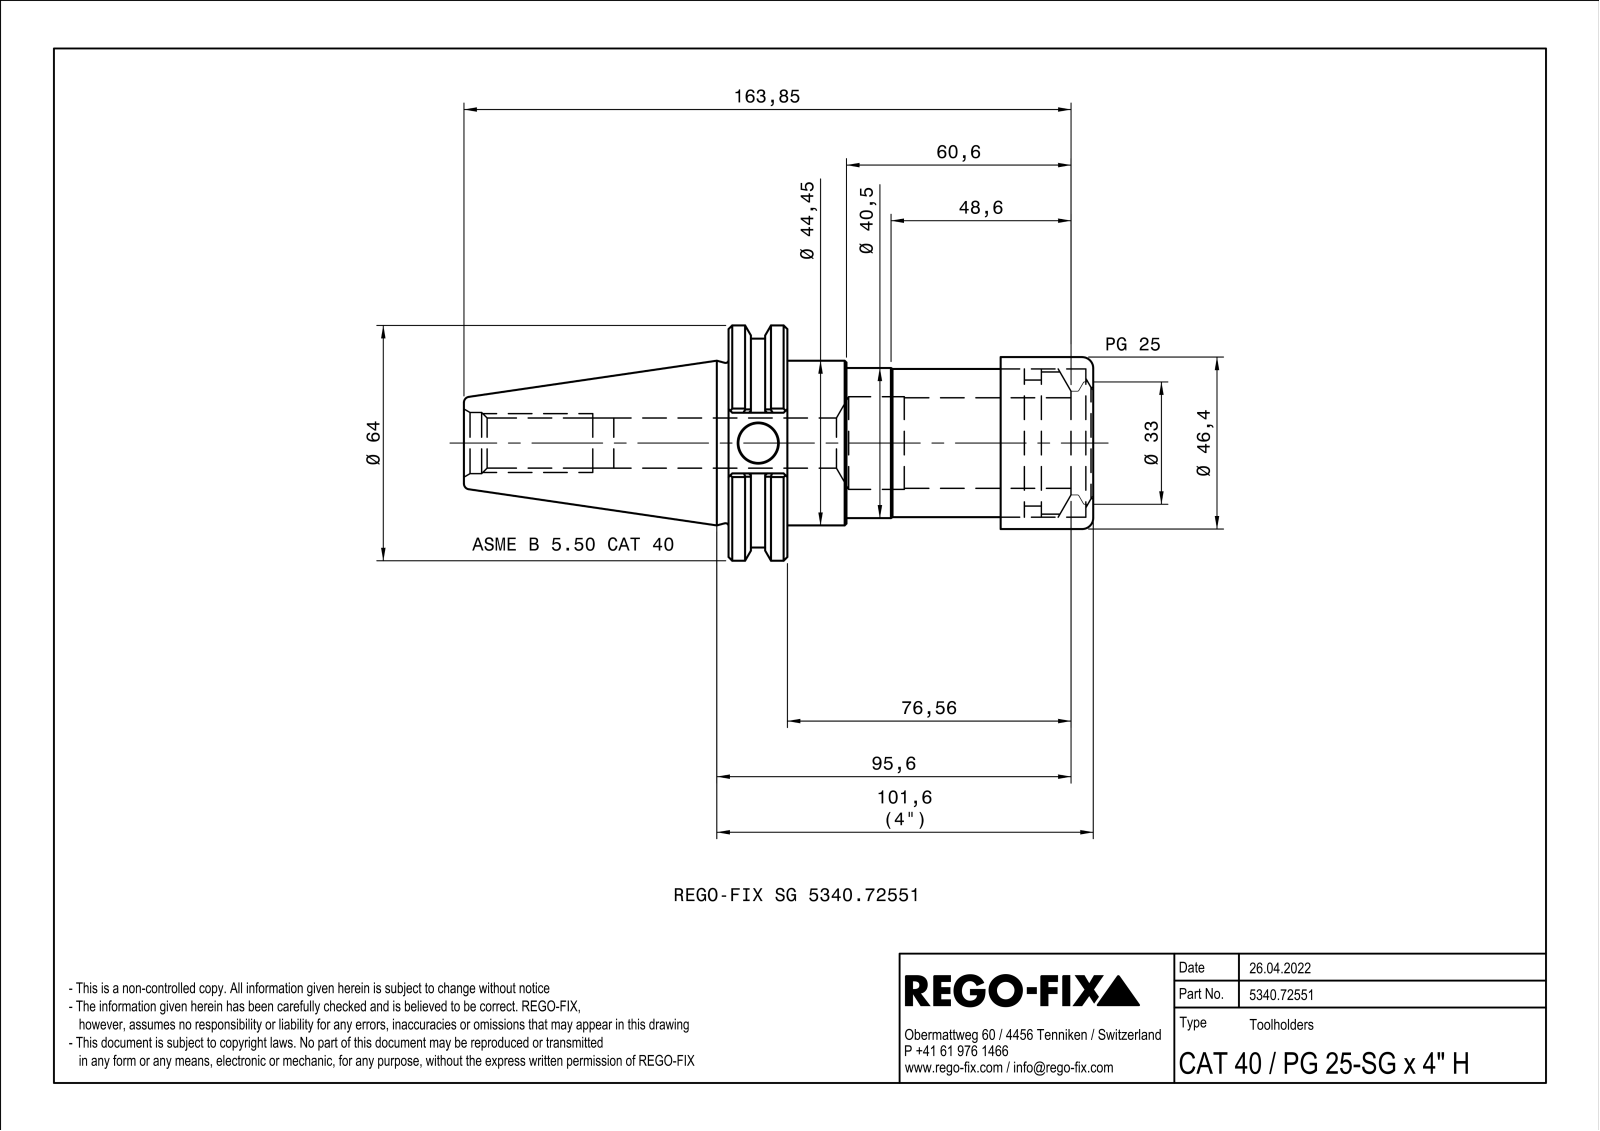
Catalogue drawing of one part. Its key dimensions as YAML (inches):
part_name: "NOCUT"
step_written_by: "SIEMENS PLM Software Solid Edge ST10 (AUTOMOTIVE_DESIGN)"
units: inches
bodies: {solids: 1, faces: 110, planar: 37, cylindrical: 23, other: 50}
overall_size: [6.687, 2.5, 2.393]
volume: 10.79
surface_area: 65.96
round_holes:
  - {diameter: 0.421, count: 1}
  - {diameter: 0.533, count: 1}
  - {diameter: 0.65, count: 1}
  - {diameter: 0.984, count: 1}
  - {diameter: 1.181, count: 1}
  - {diameter: 1.577, count: 1}
  - {diameter: 1.654, count: 1}
round_bosses_or_shafts:
  - {diameter: 2.5, count: 1}
  - {diameter: 2.219, count: 1}
  - {diameter: 1.827, count: 1}
  - {diameter: 1.811, count: 1}
  - {diameter: 1.75, count: 1}
  - {diameter: 1.594, count: 1}
  - {diameter: 1.575, count: 1}
  - {diameter: 1.339, count: 1}
partial_cylinders:
  - {radius: 0.02, count: 4}
face_to_face_distances: [0.625, 3.25, 3.875, 0.984, 2.266, 2.891, 0.732, 0.252, 2.518, 3.143]
